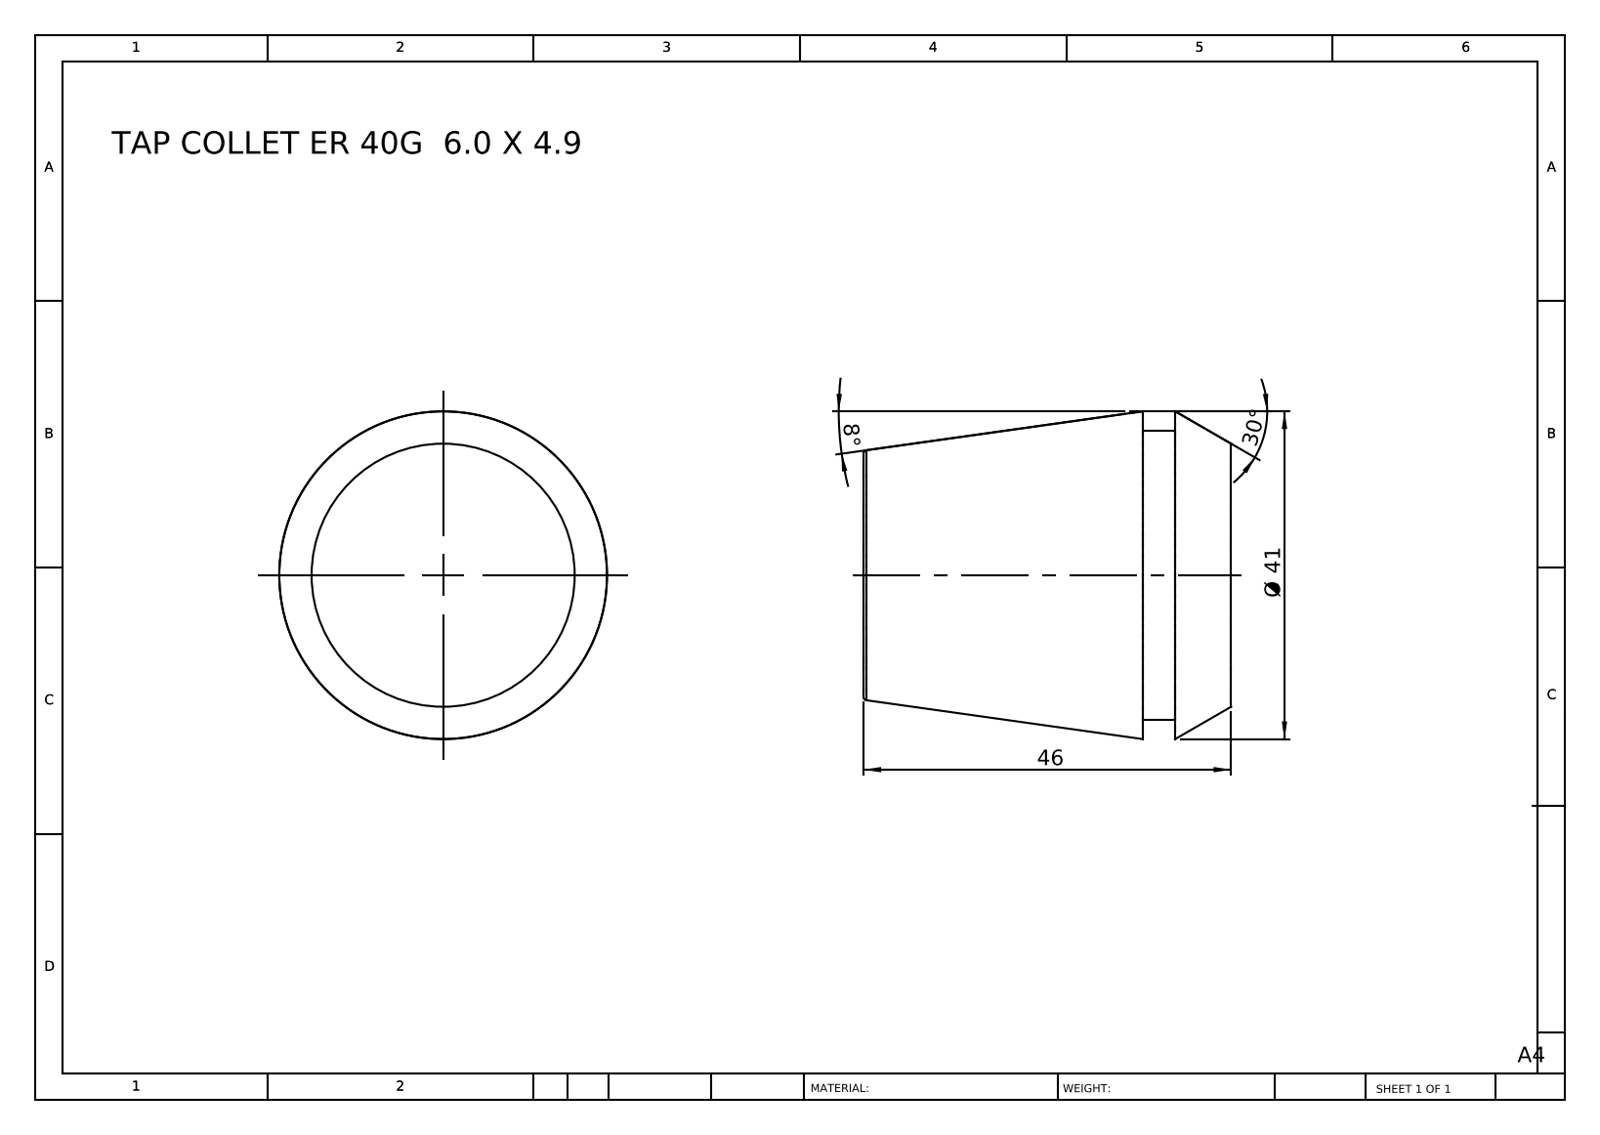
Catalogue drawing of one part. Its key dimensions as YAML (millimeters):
part_name: "TAP COLLET ER 40G 6.0 X 4.9"
step_written_by: "SolidWorks 2014 (CONFIG_CONTROL_DESIGN)"
units: millimeters
bodies: {solids: 1, faces: 12, planar: 4, cylindrical: 2, other: 6}
overall_size: [46, 41, 41]
volume: 47690
surface_area: 7586
round_bosses_or_shafts:
  - {diameter: 36.2, count: 1}
face_to_face_distances: [46, 11.1, 34.9, 7, 4.1, 39]
